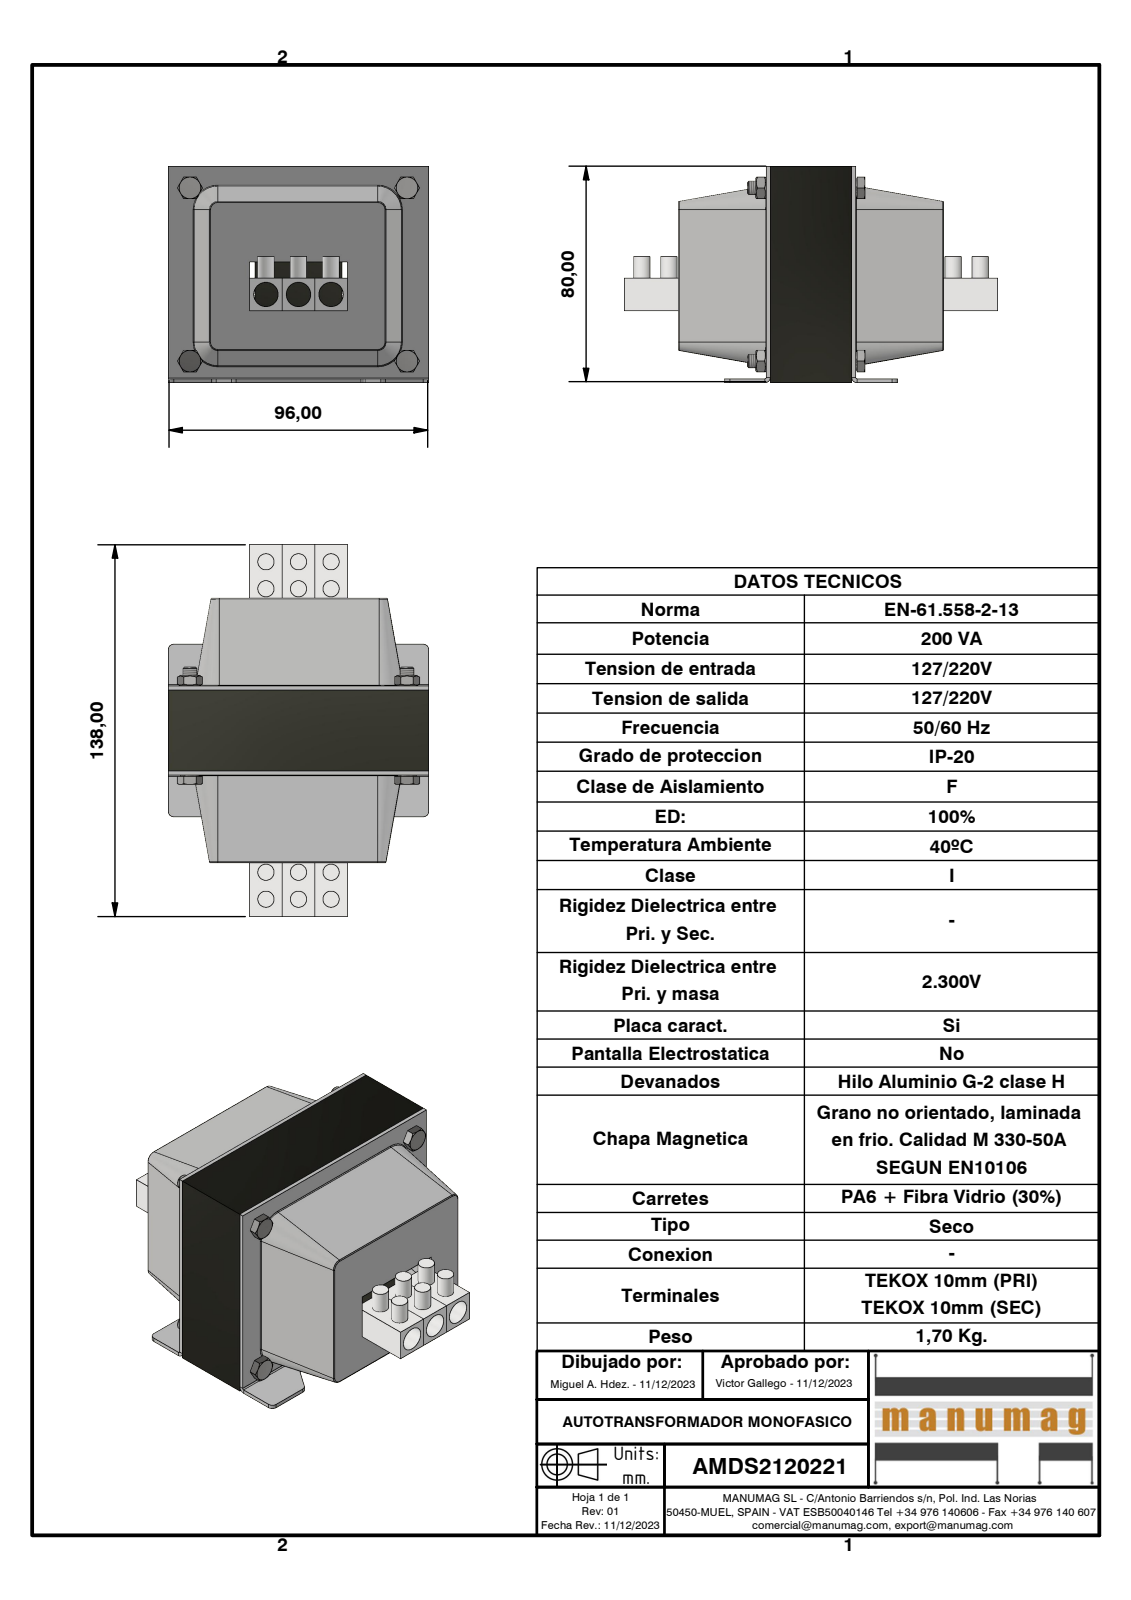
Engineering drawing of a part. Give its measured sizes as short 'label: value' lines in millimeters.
name: AMDS2120221; DIN 933 - M5 x 40; DIN 934 - M5 x 0,8; EI96 x 80 - 30 (RC32) Negro (+4 more)
written by: Autodesk Inventor 2023 (AUTOMOTIVE_DESIGN)
unit: mm
bodies: 17 solids, 352 faces (194 planar, 78 cylindrical, 80 other)
size: 138 × 96 × 80
volume: 223 260 mm³; area: 110 405 mm²
holes: 4× ⌀4.13, 4× ⌀5, 4× ⌀5.5, 3× ⌀9
bosses: 12× ⌀6, 4× ⌀6.7, 4× ⌀4.57
rounds: 16× R0.38, 14× R2, 2× R0.5
face distances: 64, 1.5, 32.5, 30, 16, 70.97, 62.5, 34, 80, 96.5
hole spacings: 12, 37.29, 46.97, 48.31, 56.12, 57.54, 64, 65.22
